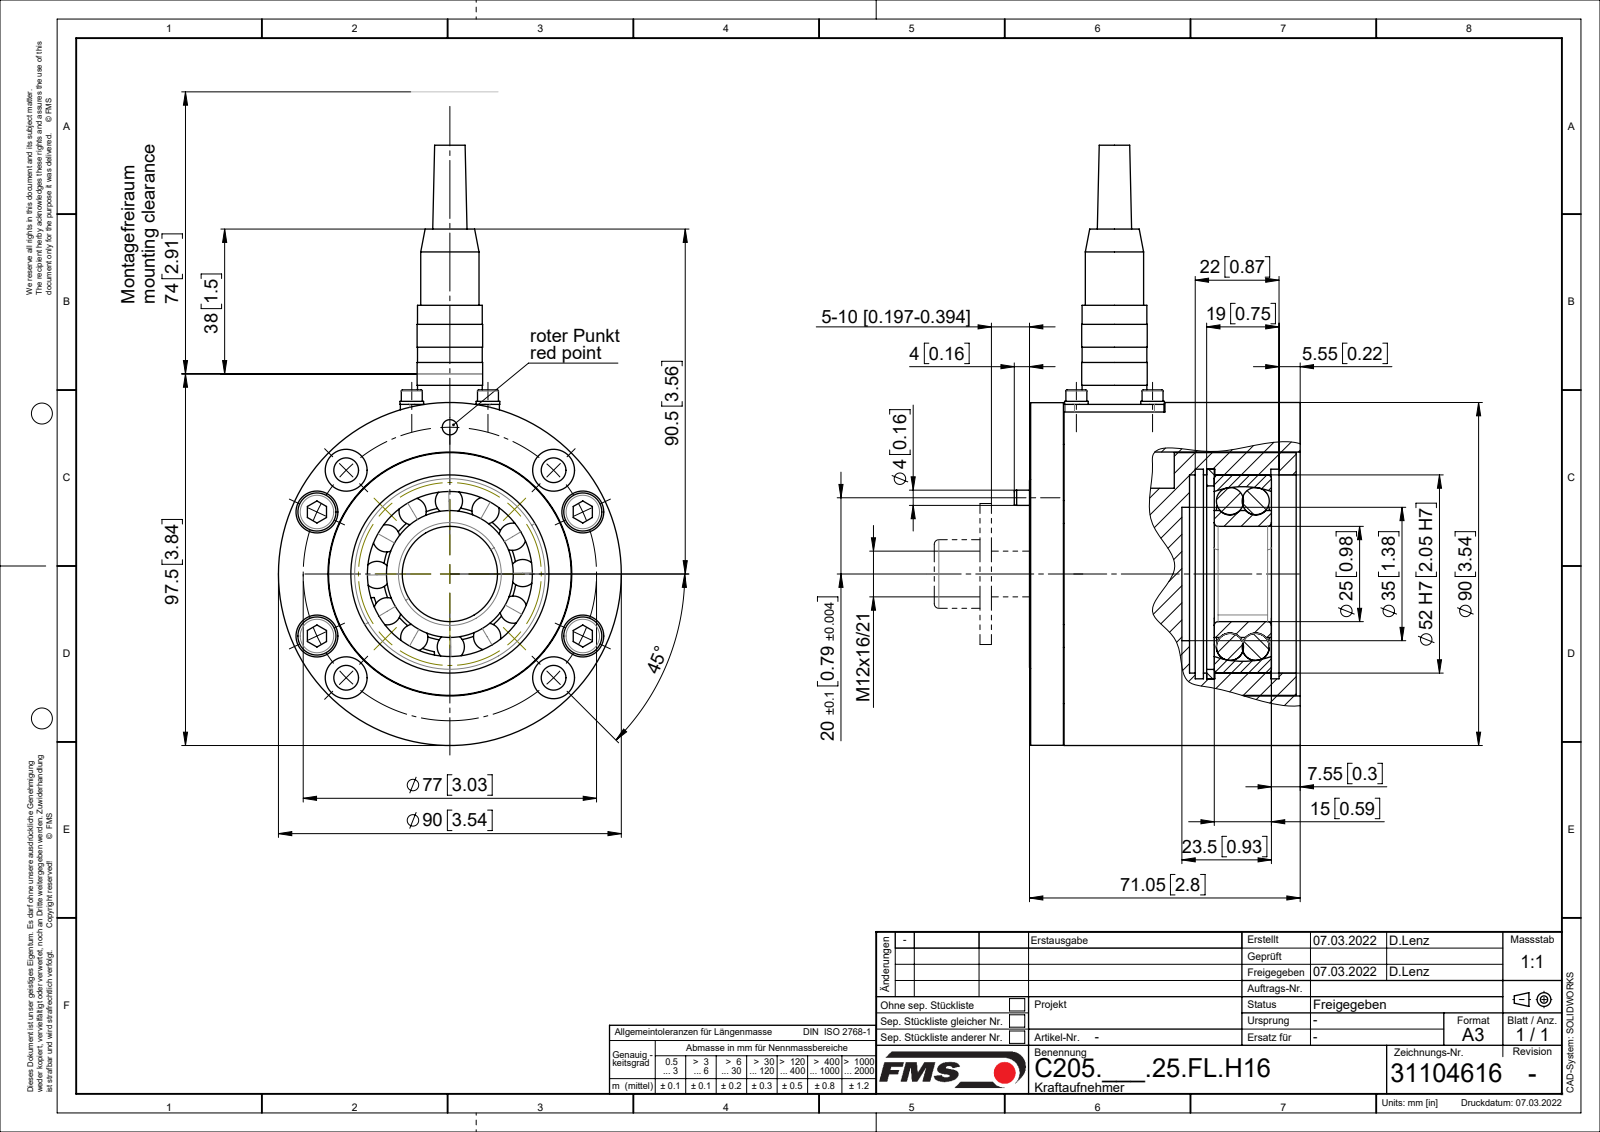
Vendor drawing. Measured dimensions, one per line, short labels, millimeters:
name: Sch DIN9021_M12; 31104484_Stp_01; Federringe_DIN127A_M03; Kabeldose_M14x1_Mini_5pol (+8 more)
written by: SolidWorks 2018 (CONFIG_CONTROL_DESIGN)
unit: mm
bodies: 47 solids, 599 faces (185 planar, 256 cylindrical, 158 other)
size: 157.5 × 96.05 × 90
volume: 318 683 mm³; area: 125 368 mm²
holes: 8× ⌀6.5, 8× ⌀11, 6× ⌀2.5, 4× ⌀3.1, 4× ⌀3.2, 4× ⌀5, 4× ⌀7, 2× ⌀4, 1× ⌀3, 1× ⌀10.2, 1× ⌀12, 1× ⌀13
bosses: 5× ⌀1.5, 4× ⌀10, 4× ⌀6.2, 4× ⌀6, 4× ⌀5.5, 4× ⌀3, 1× ⌀90, 1× ⌀89.9
rounds: 4× R0.1, 4× R2.5, 2× R0.5, 2× R4.24, 2× R5, 1× R20.8, 1× R24.1
face distances: 6, 2, 6.5, 32, 25.5, 33.05, 38, 8.6, 29.1, 37.7
hole spacings: 20, 38.5, 13.37, 14.14, 38.49, 44.16, 54.44, 63.07
